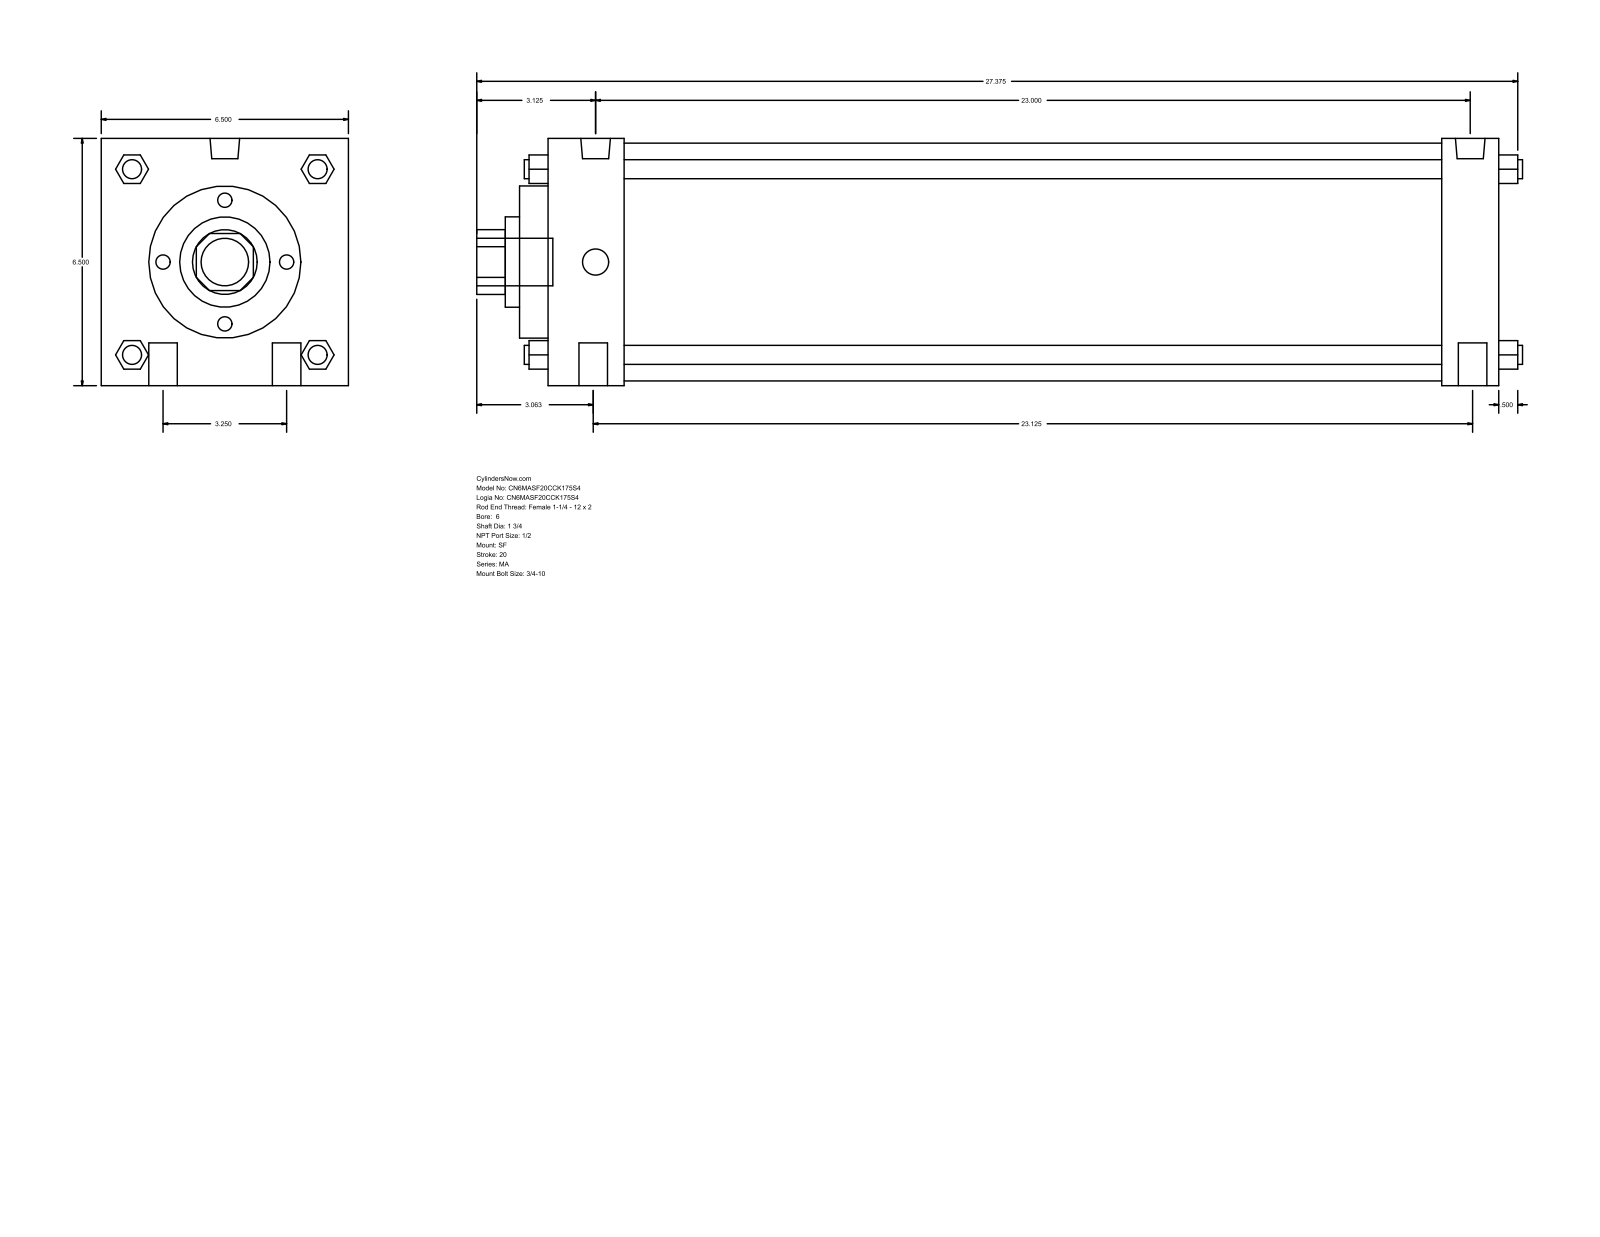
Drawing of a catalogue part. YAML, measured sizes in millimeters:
part_name: "MA_SF__0600_1.75"
step_written_by: "GSSL Pune (CONFIG_CONTROL_DESIGN)"
units: millimeters
bodies: {solids: 0, faces: 126, planar: 95, cylindrical: 31, other: 0}
overall_size: [698.5, 165.1, 165.1]
round_holes:
  - {diameter: 44.45, count: 1}
  - {diameter: 60.33, count: 1}
  - {diameter: 101.6, count: 1}
  - {diameter: 158.75, count: 1}
round_bosses_or_shafts:
  - {diameter: 19.05, count: 4}
  - {diameter: 12.7, count: 4}
  - {diameter: 19.77, count: 2}
  - {diameter: 17.46, count: 2}
  - {diameter: 31.75, count: 1}
partial_cylinders:
  - {radius: 21.63, count: 1}
face_to_face_distances: [165.1, 635, 19.05, 50.8, 38.1, 596.9, 546.1, 584.2, 69.85, 615.95]
